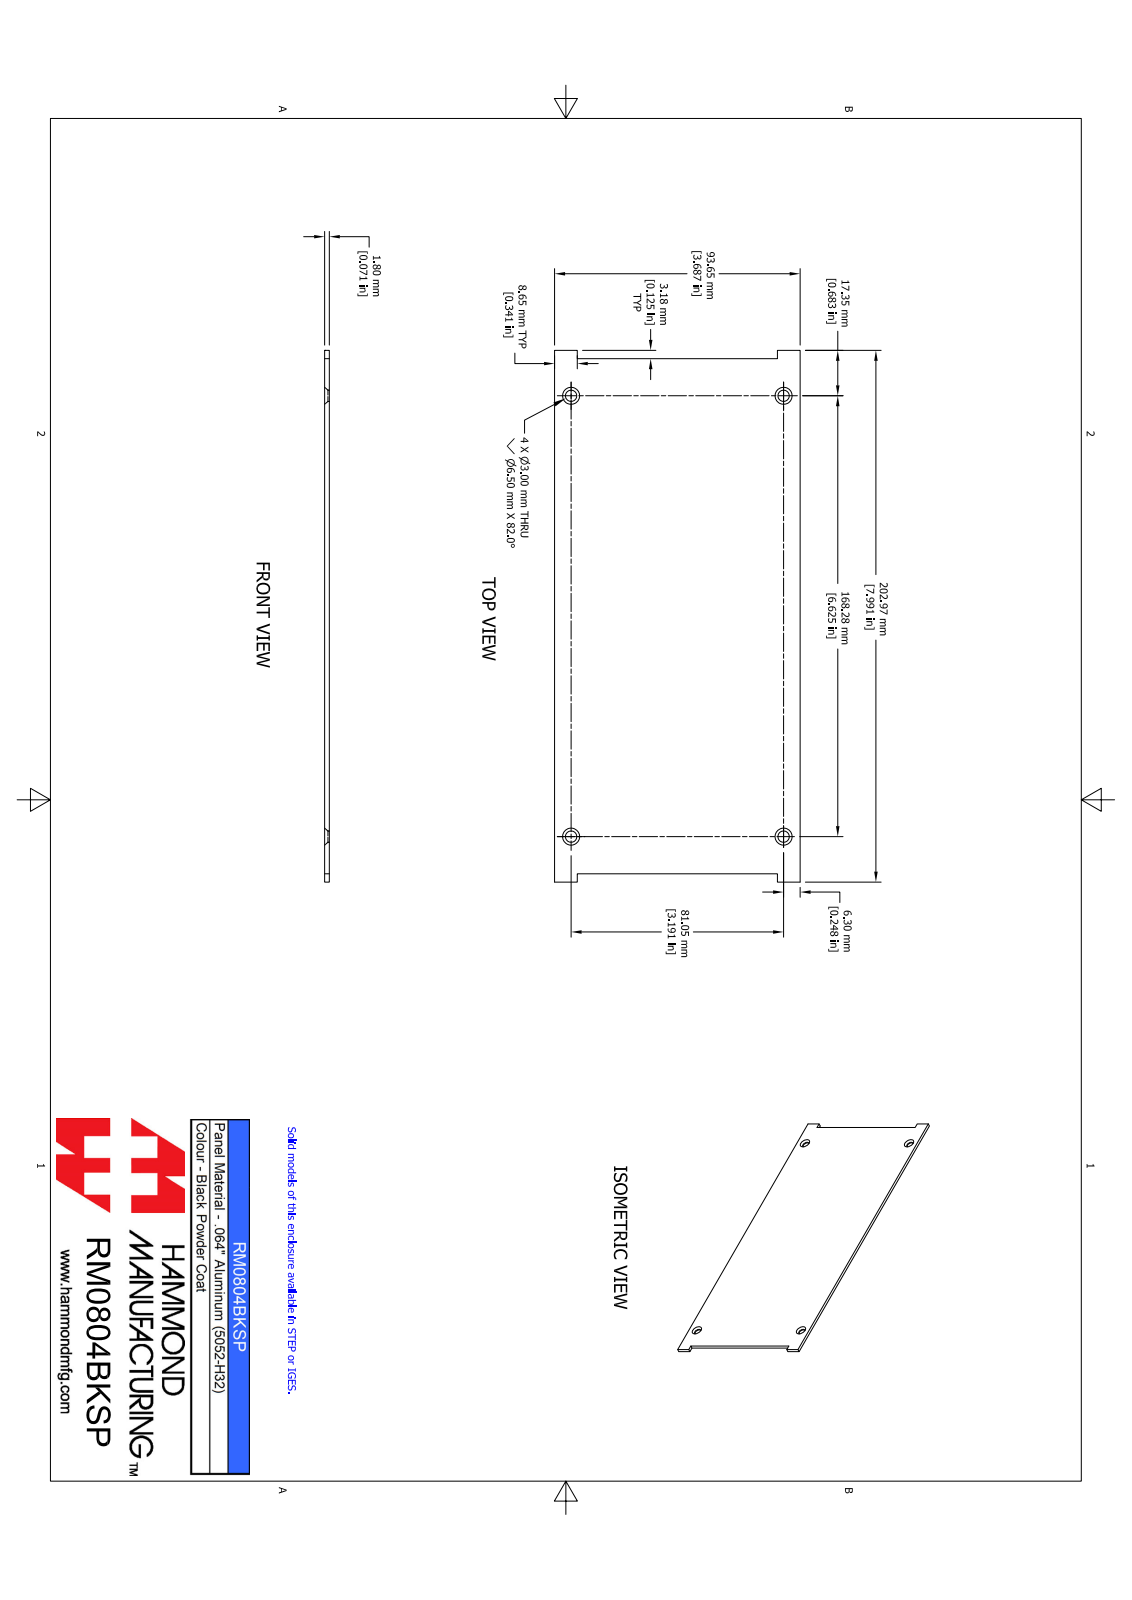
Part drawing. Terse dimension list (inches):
name: RM0804BKSP
written by: SolidWorks 2021 (AUTOMOTIVE_DESIGN)
unit: in
bodies: 1 solid, 22 faces (14 planar, 4 cylindrical, 4 other)
size: 7.991 × 3.687 × 0.071
volume: 2.026 in³; area: 59.04 in²
holes: 4× ⌀0.169
face distances: 0.071, 3.687, 7.741, 0.125, 7.866, 7.991, 0.341, 3.346, 0.341, 3.006
hole spacings: 3.191, 6.625, 7.354
